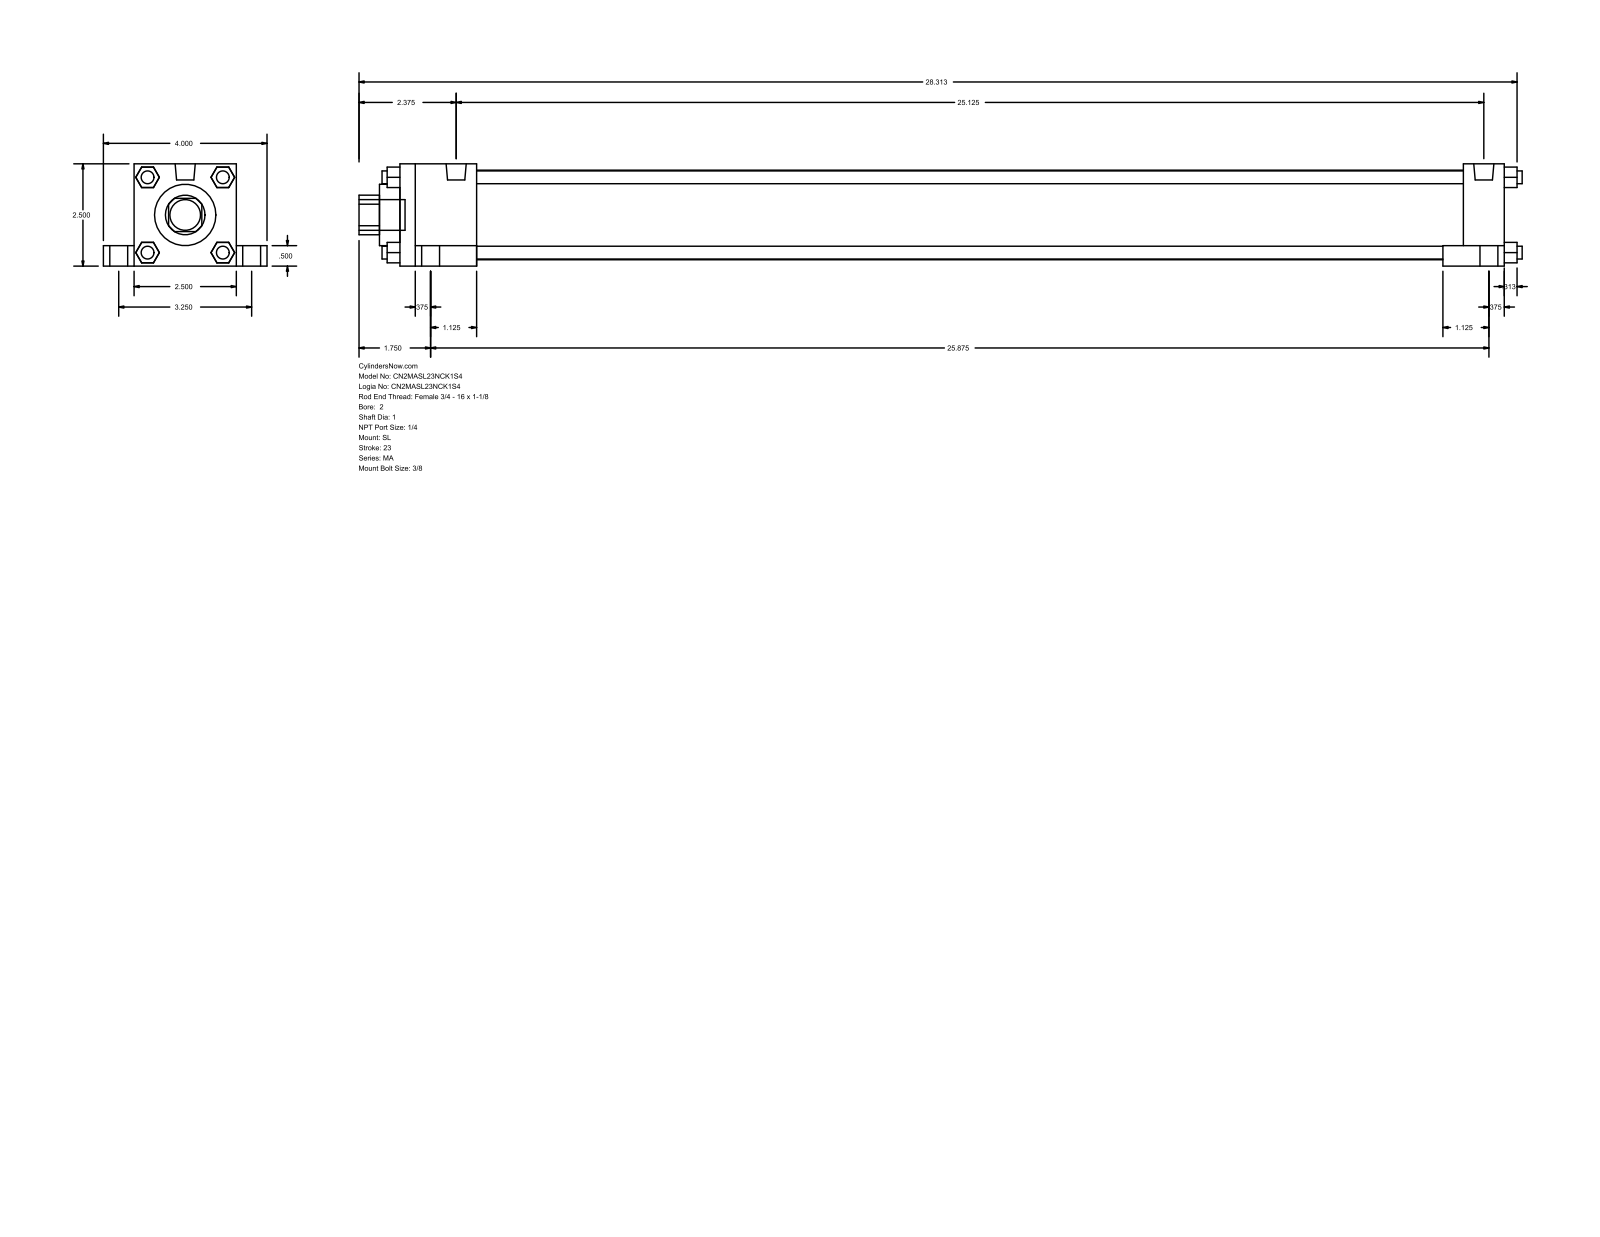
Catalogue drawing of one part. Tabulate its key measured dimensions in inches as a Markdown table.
| quantity | value |
| --- | --- |
| part name | MA_SL__0200_1 |
| STEP written by | GSSL Pune (CONFIG_CONTROL_DESIGN) |
| units | inches |
| bodies | 0 solids, 148 faces (112 planar, 36 cylindrical, 0 other) |
| overall size | 28.437 × 4 × 2.5 |
| round holes (diameter × count) | 1 × 1, 1.5 × 1, 2.19 × 1 |
| round bosses / shafts (diameter × count) | 0.313 × 8, 0.687 × 4, 0.437 × 4, 0.492 × 2, 0.75 × 1 |
| partial cylindrical surfaces (radius × count) | 0.484 × 1 |
| main face-to-face distances | 2.5, 0.5, 27, 0.75, 3.25, 1, 2, 1.875, 25.125, 26 |
